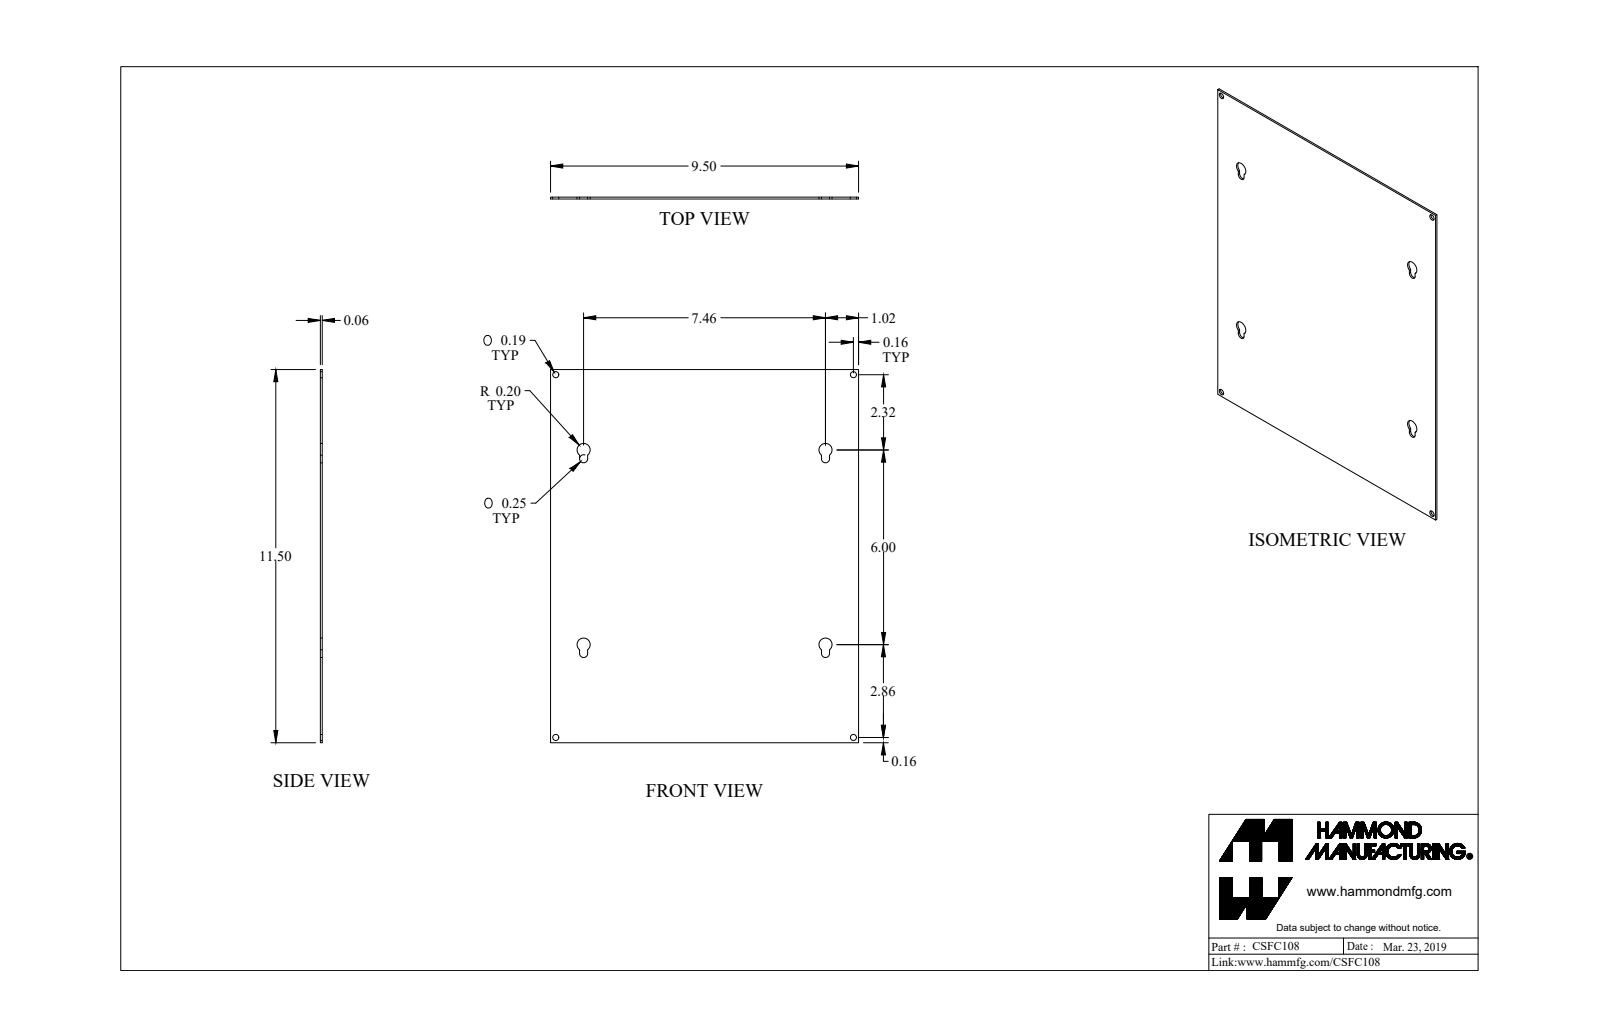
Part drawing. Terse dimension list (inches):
name: CSFC108_Default
written by: SolidWorks 2019 (CONFIG_CONTROL_DESIGN)
unit: in
bodies: 1 solid, 38 faces (14 planar, 24 cylindrical, 0 other)
size: 11.5 × 9.5 × 0.057
volume: 6.181 in³; area: 219.8 in²
holes: 4× ⌀0.188
rounds: 4× R0.125, 4× R0.203
face distances: 0.057, 9.5, 11.5, 1.145, 8.355, 0.895, 8.605, 0.25, 7.46, 7.21
hole spacings: 9.18, 11.18, 14.467
